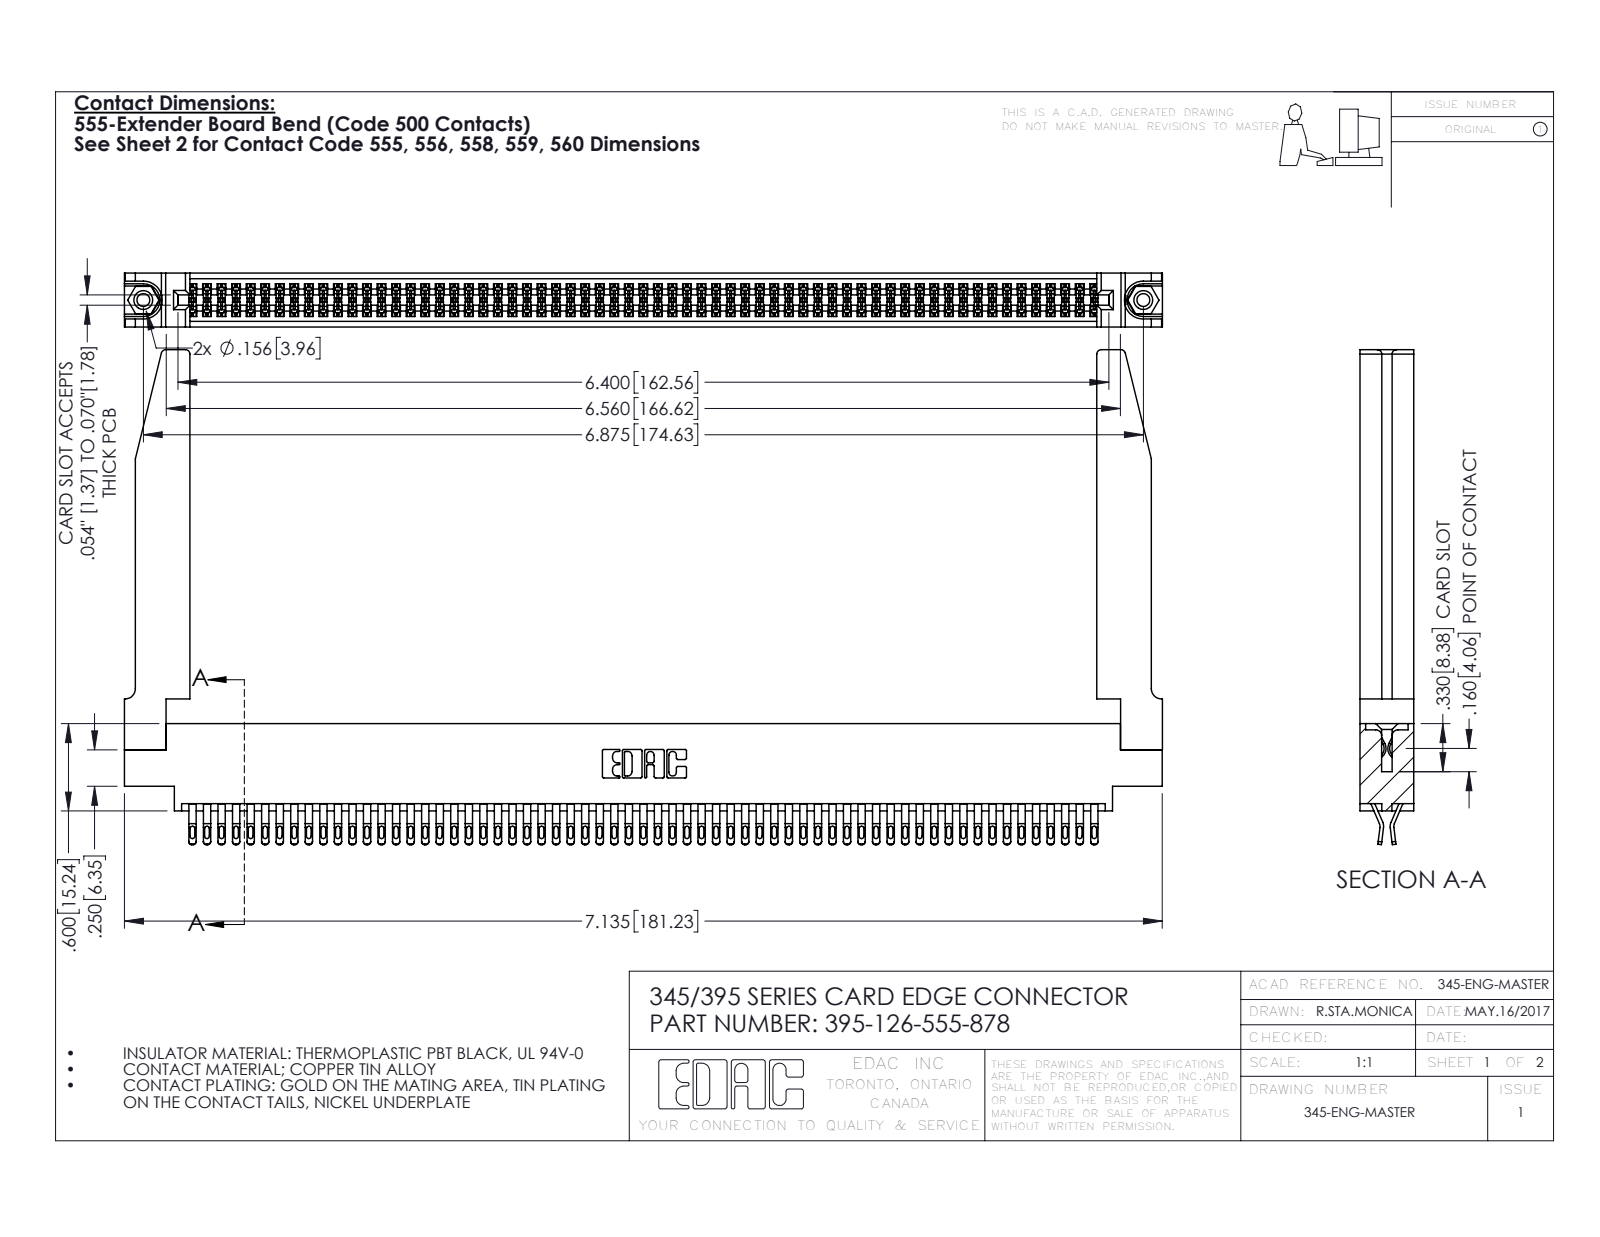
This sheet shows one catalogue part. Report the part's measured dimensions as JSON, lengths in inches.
{"part_name": "345-250-001_345-250-001-102; 345 Part_0.170 Offset - 0.156 Dia-TH; 395-126-555-878; 345-220-078_345-220-078 (+1 more)", "step_written_by": "SolidWorks 2016 (CONFIG_CONTROL_DESIGN)", "units": "inches", "bodies": {"solids": 131, "faces": 7420, "planar": 4132, "cylindrical": 3236, "other": 52}, "overall_size": [7.136, 3.402, 0.37], "volume_in3": 1.576, "surface_area_in2": 54.79, "round_holes": [[0.089, 2], [0.125, 2], [0.156, 2], [0.064, 1]], "round_bosses_or_shafts": [[0.155, 2]], "partial_cylinders_radius": [[0.016, 315], [0.02, 252], [0.006, 189], [0.01, 22], [0.03, 8], [0.007, 6], [0.031, 6], [0.026, 3]], "face_to_face_distances": [0.072, 0.37, 0.298, 0.025, 0.098, 0.272, 0.2, 0.225, 0.175, 0.148], "hole_center_spacings": [0.27, 6.639, 6.875]}
